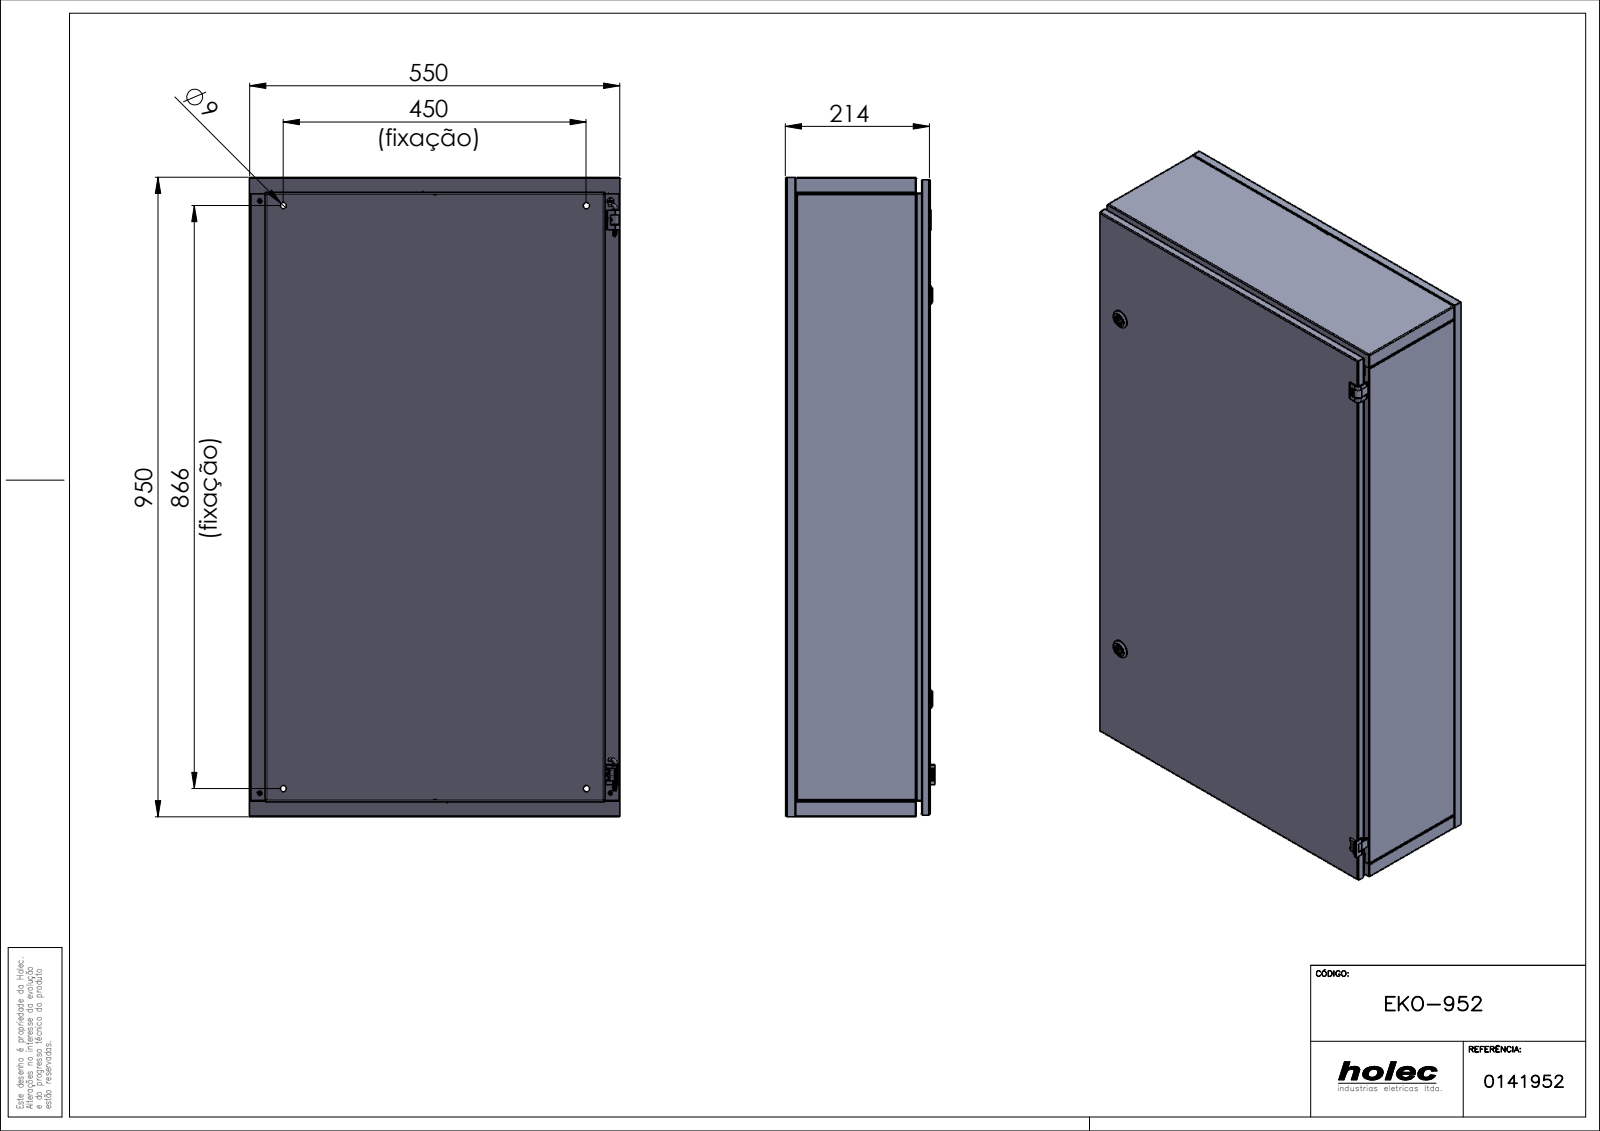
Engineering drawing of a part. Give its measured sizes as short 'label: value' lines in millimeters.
name: EKO-952
written by: SolidWorks 2017 (AUTOMOTIVE_DESIGN)
unit: mm
bodies: 61 solids, 2930 faces (1398 planar, 920 cylindrical, 612 other)
size: 950 × 550 × 220.88
volume: 2 087 000 mm³; area: 4 120 000 mm²
holes: 24× ⌀4.3, 19× ⌀4.2, 18× ⌀6, 10× ⌀7.52, 9× ⌀1.8, 6× ⌀5.5, 6× ⌀11, 4× ⌀5, 4× ⌀9, 2× ⌀3.3, 2× ⌀4, 2× ⌀4.1
bosses: 10× ⌀7, 9× ⌀3.2, 2× ⌀28, 2× ⌀19, 2× ⌀15.7, 2× ⌀15, 2× ⌀12.7, 2× ⌀5.15
rounds: 88× R0.2, 50× R1.5, 48× R0.5, 20× R0.3, 16× R1, 10× R2.5, 6× R2, 4× R1.05
face distances: 1, 213.1, 214.1, 212.1, 549, 949, 550, 548, 24, 20.1
hole spacings: 25, 50, 75, 230.5, 249.5, 31.4, 231.8, 231.91
